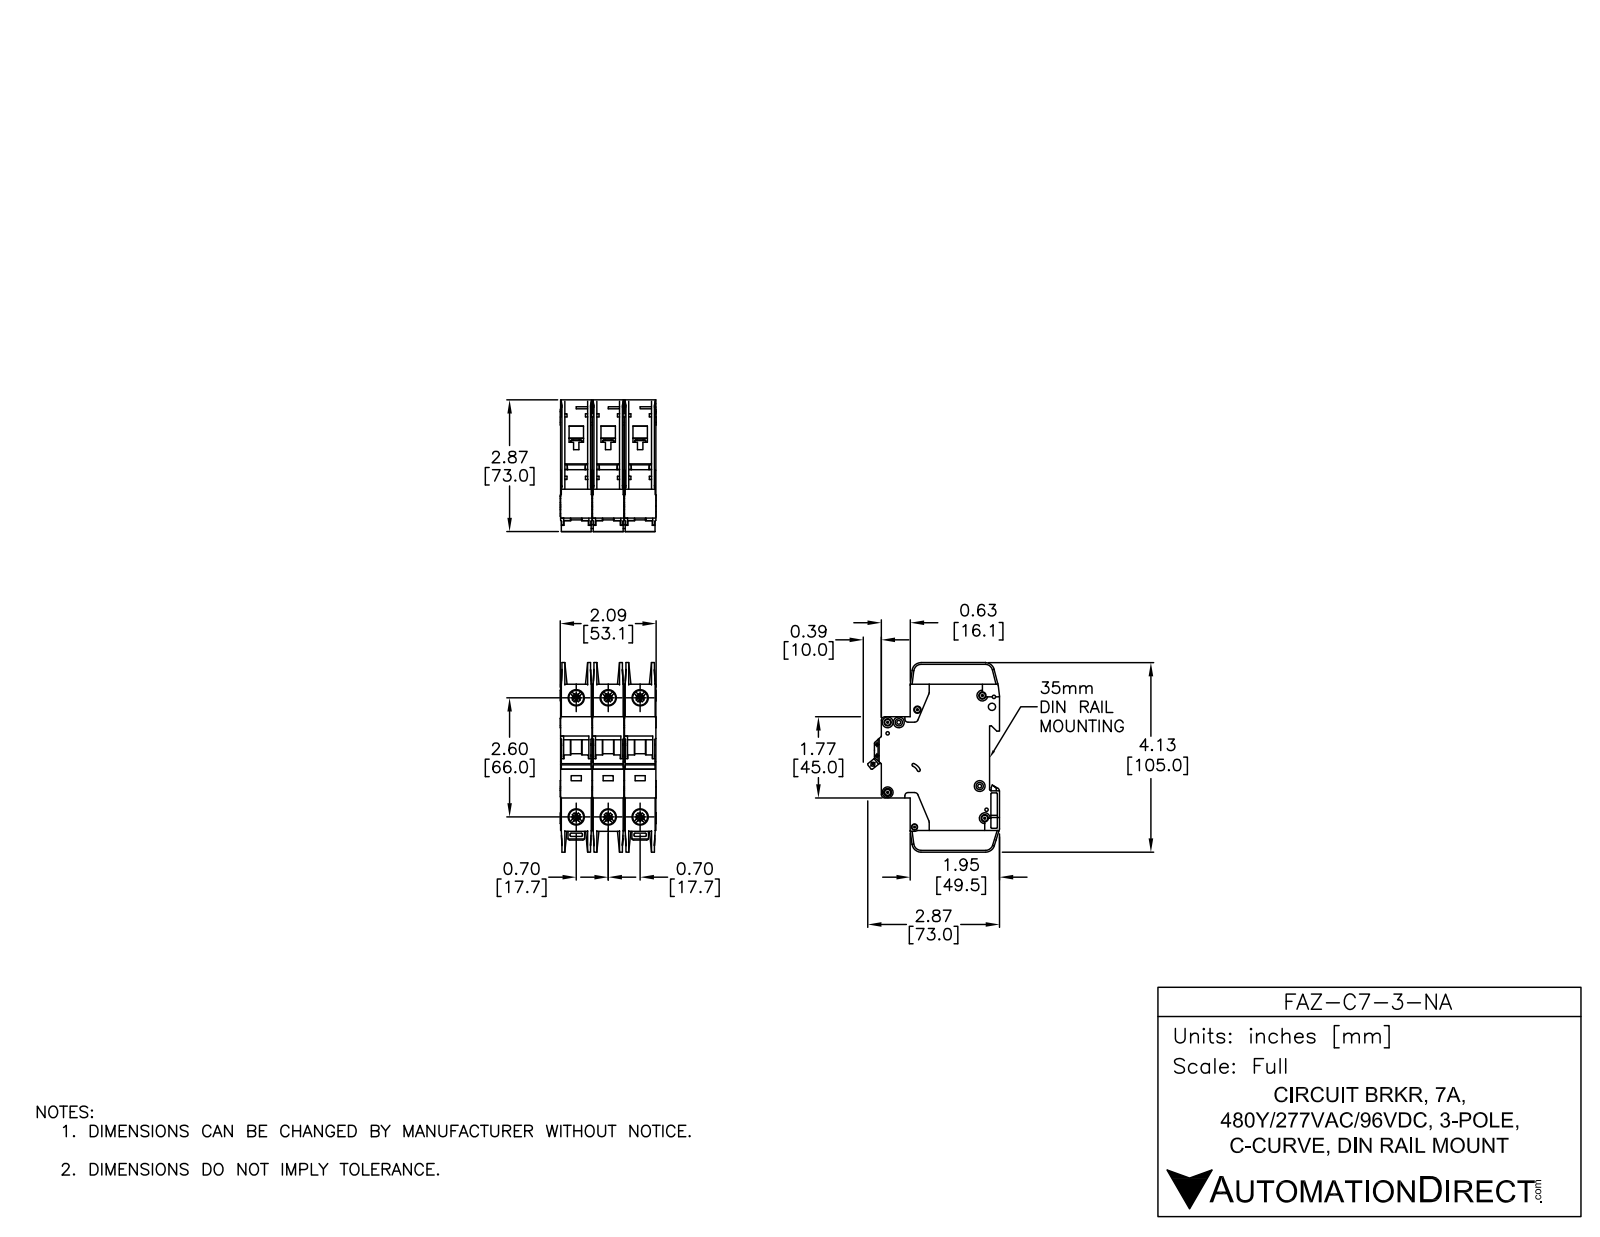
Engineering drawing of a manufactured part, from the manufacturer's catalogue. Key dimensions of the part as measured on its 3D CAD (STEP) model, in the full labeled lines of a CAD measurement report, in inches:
Part name (STEP PRODUCT): FAZ-C7-3-NA
STEP written by: SolidWorks 2014 (AUTOMOTIVE_DESIGN)
Units: inches
Bodies: 9 solids, 2352 faces (1227 planar, 789 cylindrical, 336 other)
Overall size (bounding box): 4.134 × 2.876 × 2.091
Volume: 14.22 in³ · Surface area: 115 in²
Round holes (diameter × count): ⌀0.142 ×7, ⌀0.281 ×6, ⌀0.323 ×6, ⌀0.043 ×2, ⌀0.059 ×2, ⌀0.157 ×2, ⌀0.075 ×1, ⌀0.085 ×1, ⌀0.087 ×1, ⌀0.1 ×1, ⌀0.13 ×1, ⌀0.134 ×1
Round bosses / shafts (diameter × count): ⌀0.236 ×7, ⌀0.098 ×3
Partial cylindrical surfaces — rounded edges, fillets, slot ends (radius × count): R0.01 ×65, R0.02 ×30, R0.039 ×26, R0.079 ×14, R0.071 ×5, R0.197 ×5, R0.157 ×4, R0.008 ×2
Main face-to-face distances: 0.697, 1.394, 0.689, 1.386, 0.028, 0.593, 0.096, 0.069, 0.62, 0.524
Hole centre spacings: 0.697, 2.69, 2.598, 0.244, 1.394, 2.948, 0.204, 0.24
